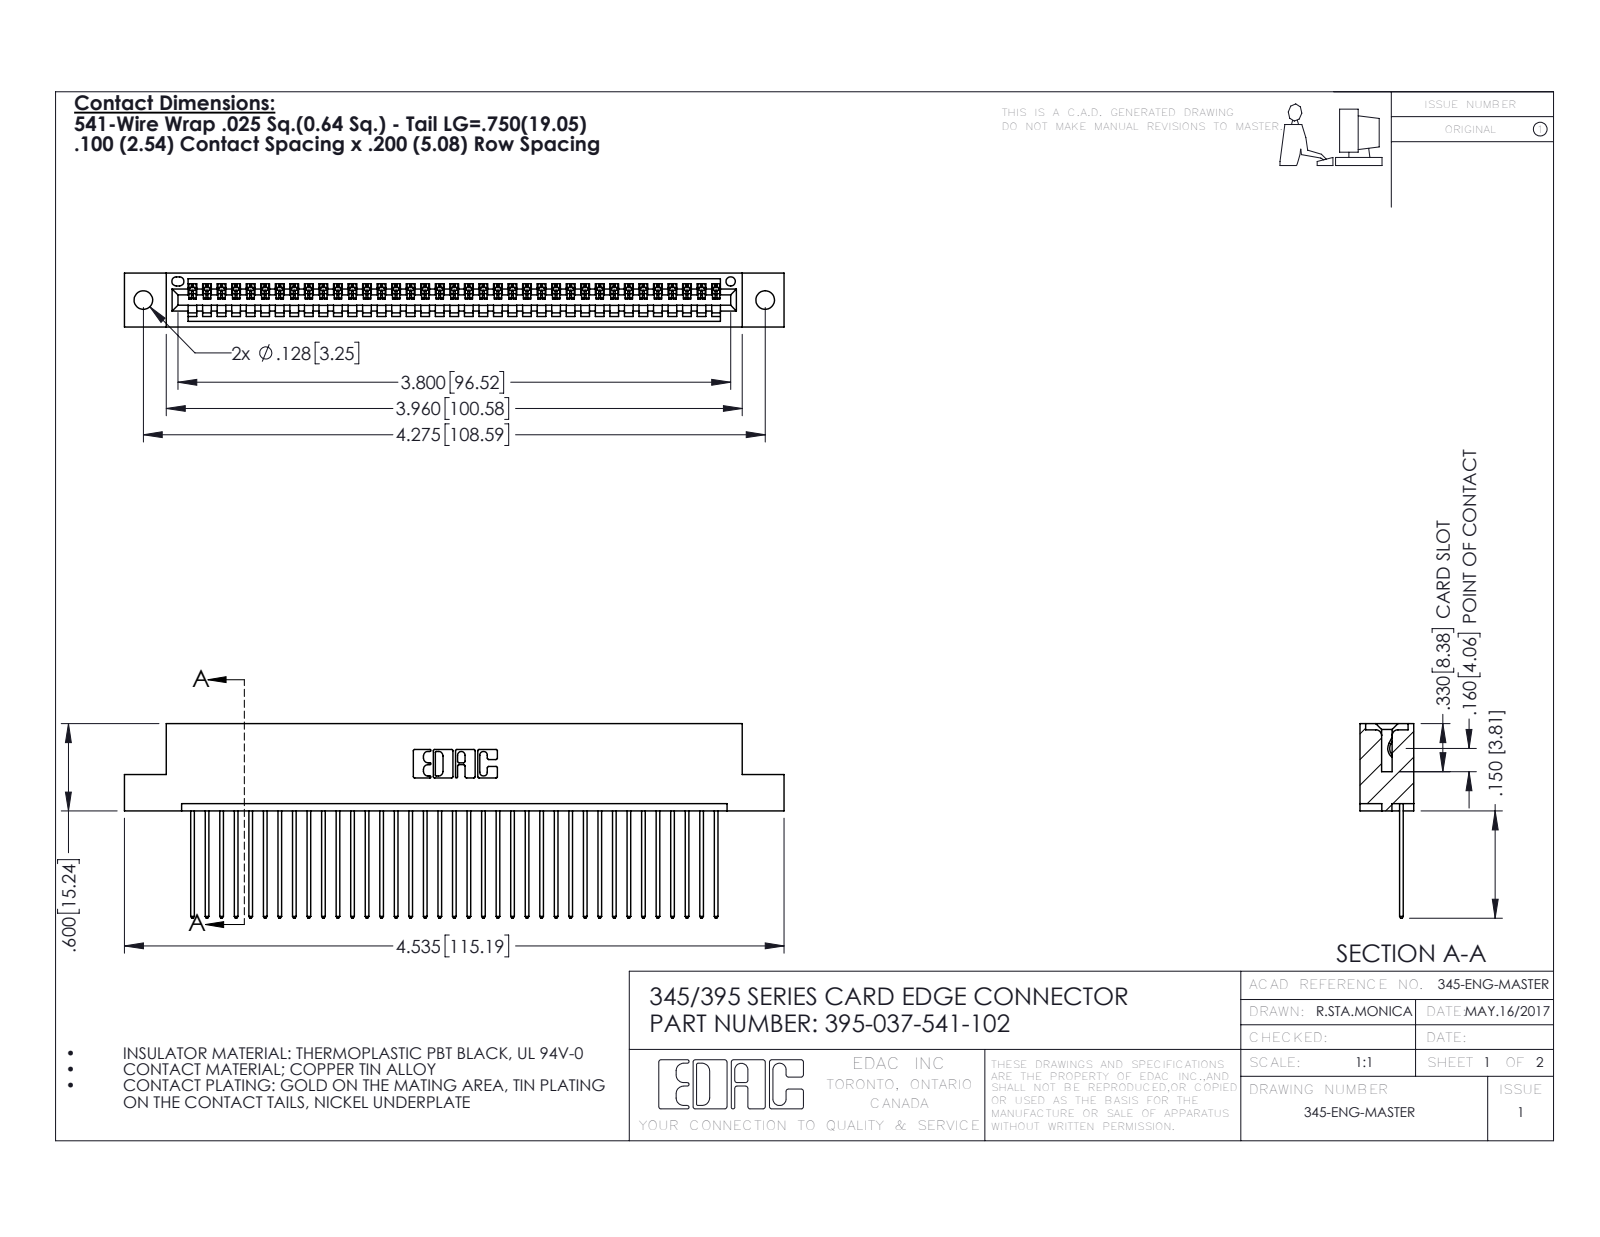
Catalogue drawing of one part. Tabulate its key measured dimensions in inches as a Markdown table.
| quantity | value |
| --- | --- |
| part name | 345-292-001_345-293-141; 395-037-541-102; 345 Part_Flush Mounting Lugs - 0.128 Dia |
| STEP written by | SolidWorks 2016 (CONFIG_CONTROL_DESIGN) |
| units | inches |
| bodies | 38 solids, 2272 faces (1560 planar, 712 cylindrical, 0 other) |
| overall size | 4.535 × 1.337 × 0.37 |
| volume | 0.67 in³ |
| surface area | 23.21 in² |
| round holes (diameter × count) | 0.128 × 2, 0.064 × 1 |
| partial cylindrical surfaces (radius × count) | 0.006 × 74, 0.01 × 74, 0.01 × 22, 0.007 × 6, 0.031 × 6, 0.026 × 3, 0.031 × 2, 0.04 × 2 |
| main face-to-face distances | 0.072, 0.298, 0.098, 0.272, 0.025, 0.2, 0.37, 0.225, 0.149, 0.072 |
| hole center spacings | 0.27, 4.039, 4.275 |
